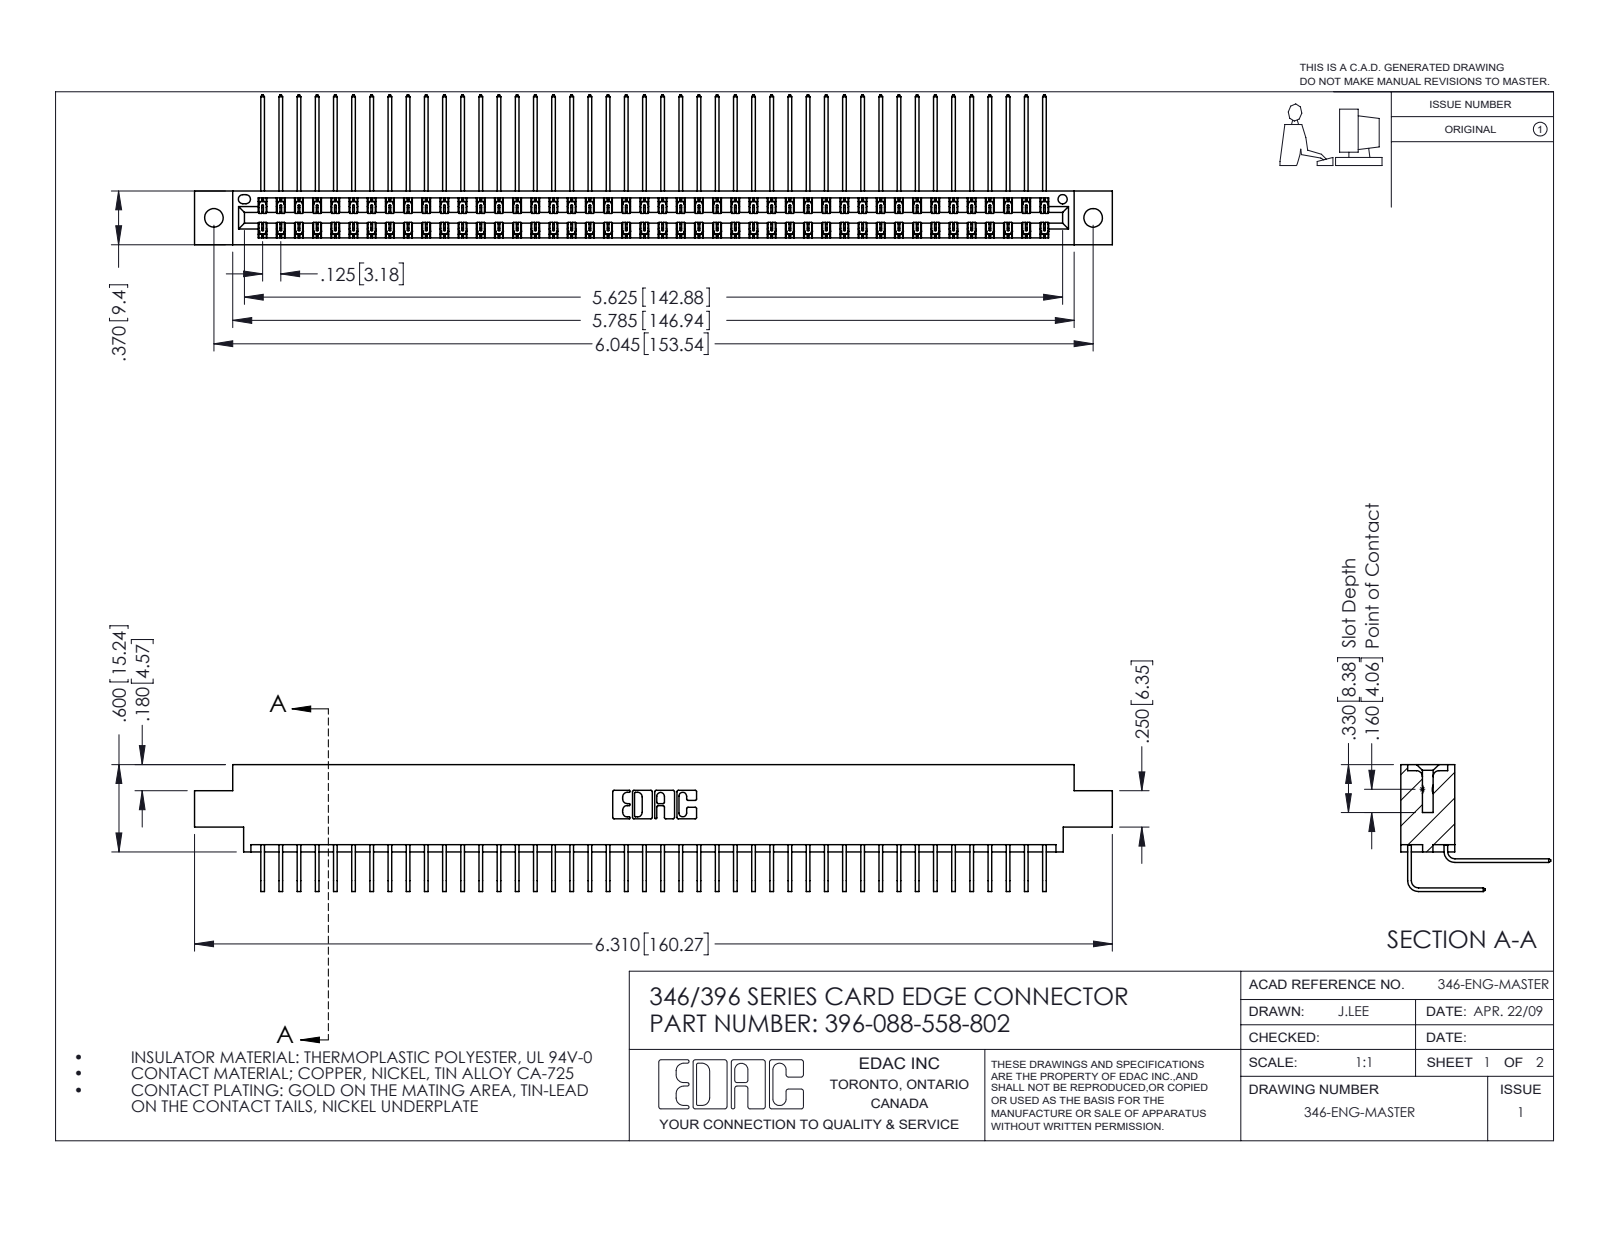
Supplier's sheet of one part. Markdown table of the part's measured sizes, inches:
| quantity | value |
| --- | --- |
| part name | 396-088-558-802; 345-292-001_558 559 Tail - 1; 346 Part_0.170 Offset - 0.128 Dia; 345-292-001_558 Tail - 2 |
| STEP written by | SolidWorks 2016 (CONFIG_CONTROL_DESIGN) |
| units | inches |
| bodies | 89 solids, 4878 faces (3336 planar, 1542 cylindrical, 0 other) |
| overall size | 6.31 × 1.03 × 0.873 |
| volume | 0.974 in³ |
| surface area | 37.69 in² |
| round holes (diameter × count) | 0.128 × 2, 0.064 × 1 |
| partial cylindrical surfaces (radius × count) | 0.006 × 132, 0.01 × 22, 0.007 × 6, 0.031 × 6, 0.026 × 3, 0.014 × 2, 0.022 × 2, 0.024 × 2 |
| main face-to-face distances | 0.322, 0.048, 0.025, 0.37, 0.25, 0.298, 0.072, 0.275, 0.148, 0.222 |
| hole center spacings | 0.246, 5.836, 6.045 |
